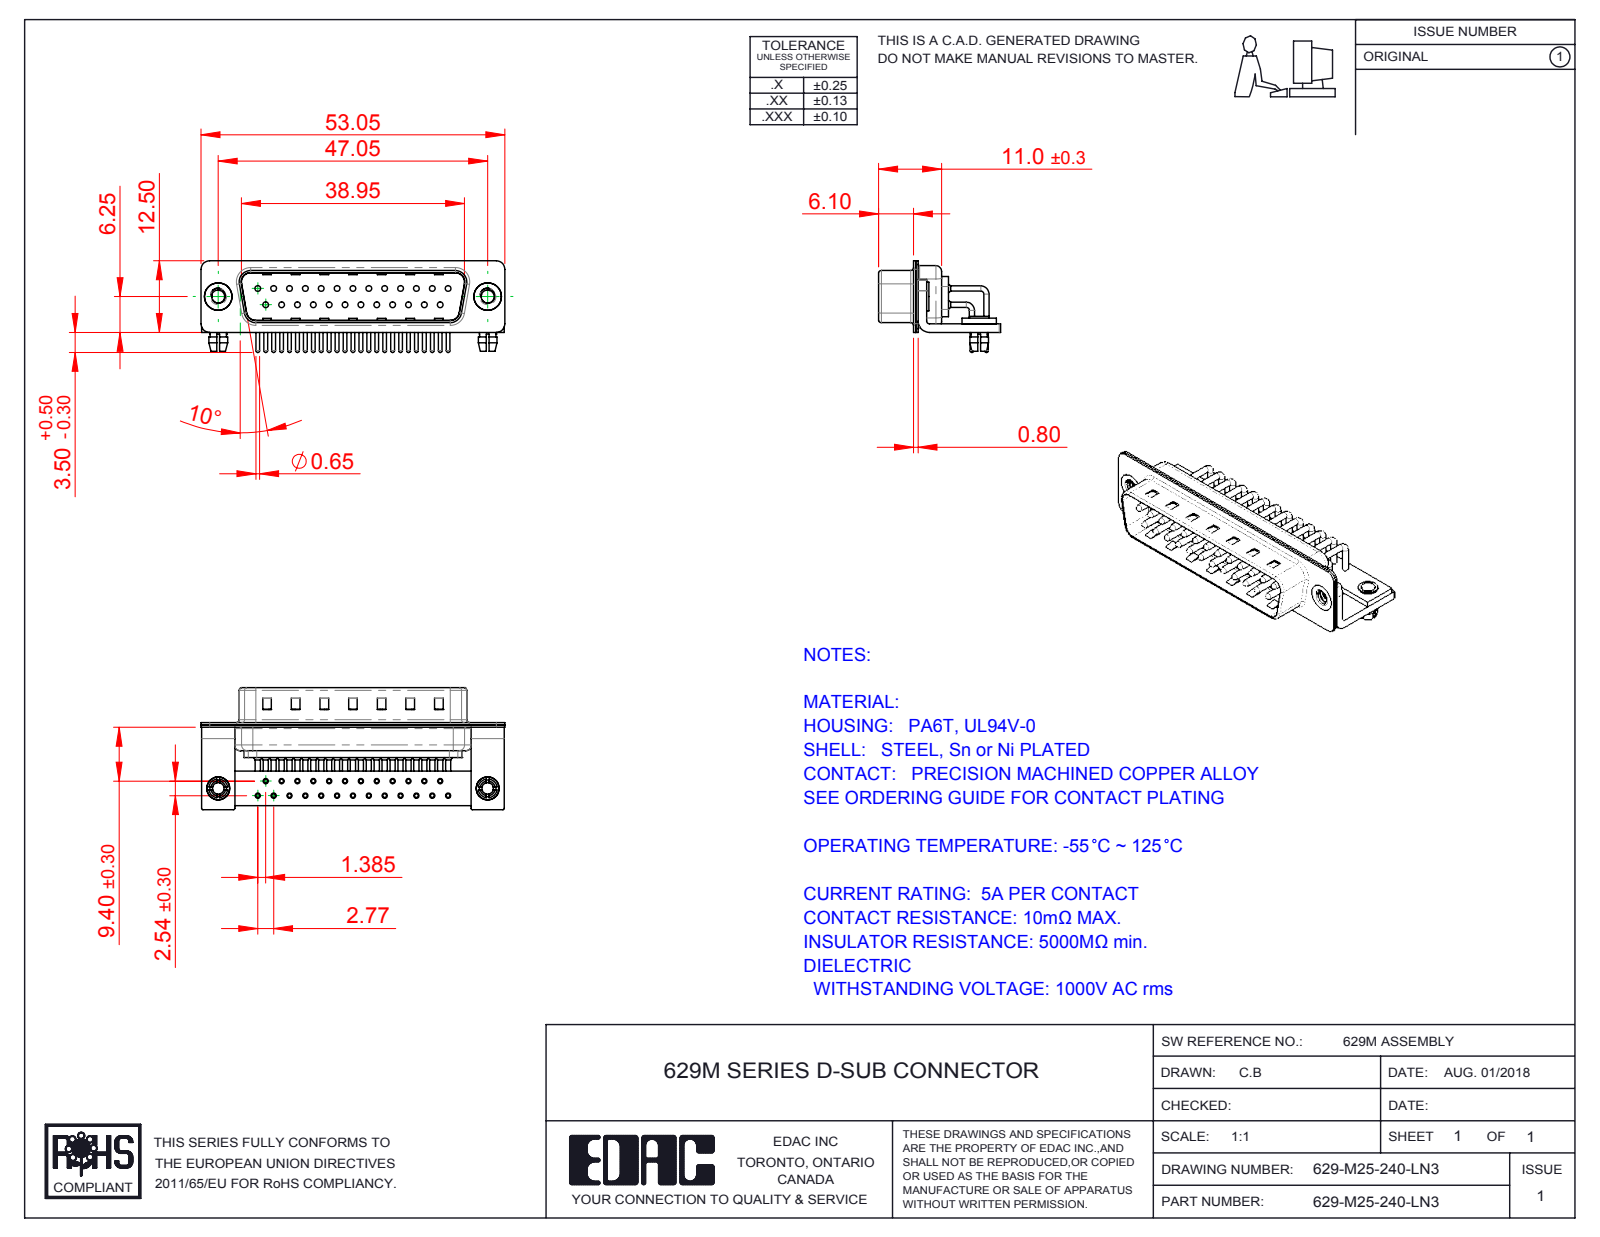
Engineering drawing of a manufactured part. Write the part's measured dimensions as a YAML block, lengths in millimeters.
part_name: "629M Board Lock; 629M Stabilizer Board_25 Contacts; 629M Stabilizer Bracket; 629M 4-40 Threaded Rivet_Stabilizer (+6 more)"
step_written_by: "SolidWorks 2016 (CONFIG_CONTROL_DESIGN)"
units: millimeters
bodies: {solids: 35, faces: 3318, planar: 1845, cylindrical: 1141, other: 332}
overall_size: [53.05, 21.3, 16]
volume: 3509
surface_area: 9368
round_holes:
  - {diameter: 2, count: 27}
  - {diameter: 0.9, count: 25}
  - {diameter: 1, count: 25}
  - {diameter: 1.7, count: 25}
  - {diameter: 2.26, count: 2}
  - {diameter: 2.5, count: 2}
  - {diameter: 3.2, count: 2}
  - {diameter: 4, count: 2}
  - {diameter: 4.8, count: 2}
round_bosses_or_shafts:
  - {diameter: 1.5, count: 25}
  - {diameter: 0.9, count: 25}
  - {diameter: 0.65, count: 25}
  - {diameter: 5, count: 2}
  - {diameter: 4.9, count: 2}
  - {diameter: 4, count: 2}
  - {diameter: 3.4, count: 2}
  - {diameter: 3.3, count: 2}
partial_cylinders:
  - {radius: 1.01, count: 25}
  - {radius: 0.25, count: 16}
  - {radius: 1.5, count: 16}
  - {radius: 2, count: 13}
  - {radius: 0.5, count: 9}
  - {radius: 1.6, count: 8}
  - {radius: 0.6, count: 4}
  - {radius: 0.65, count: 4}
face_to_face_distances: [0.4, 0.85, 1.25, 1.5, 0.8, 9.55, 10.4, 1, 1.9, 8.3]
hole_center_spacings: [2.77, 5.54, 8.31, 11.08, 13.85, 3.16, 4.87, 16.62]
